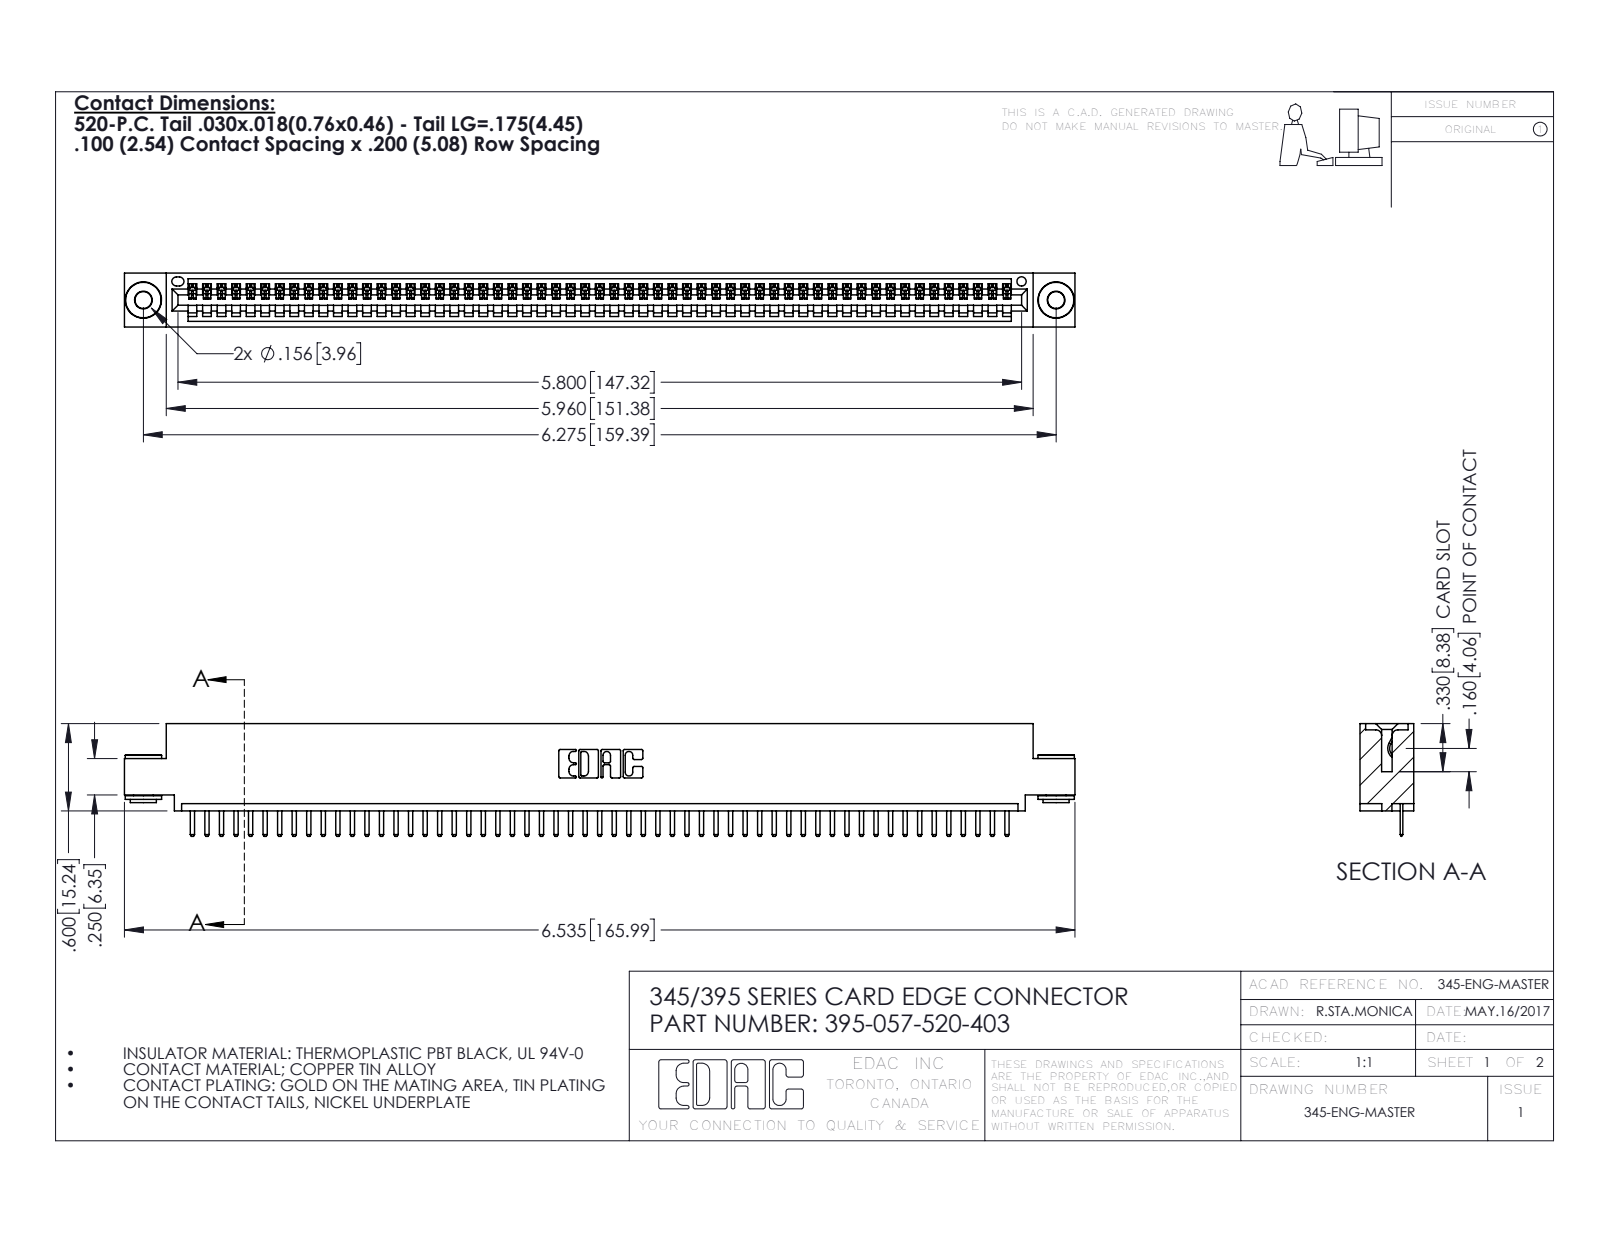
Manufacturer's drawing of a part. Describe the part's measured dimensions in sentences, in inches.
The part is named "395-057-520-403; 345 Part_0.110 Offset - 0.156 Dia-TH; 345-292-001_345-293-120; 345-250-002_345-250-002-102". Its 3-D file was written by "SolidWorks 2016 (CONFIG_CONTROL_DESIGN)". It is 60 solids with 3702 faces: 2488 planar, 1206 cylindrical and 8 other. Overall it measures 6.535 by 0.775 by 0.37 inches. Its volume is 0.956 cubic inches and its surface area 32.22 square inches. Round holes: 2 of diameter 0.116, 2 of diameter 0.156, 1 of diameter 0.064. Round bosses or shafts: 2 of diameter 0.25, 2 of diameter 0.18, 2 of diameter 0.136. Partial cylindrical surfaces (rounded edges, fillets, slot ends): 116 of radius 0.01, 114 of radius 0.006, 22 of radius 0.01, 6 of radius 0.007, 6 of radius 0.031, 3 of radius 0.026, 2 of radius 0.031, 2 of radius 0.04. The main face-to-face distances are 0.072, 0.298, 0.37, 0.2, 0.025, 0.098, 0.272, 0.225, 0.072, 0.149. The hole center spacings are 0.27, 6.039, 6.275.
